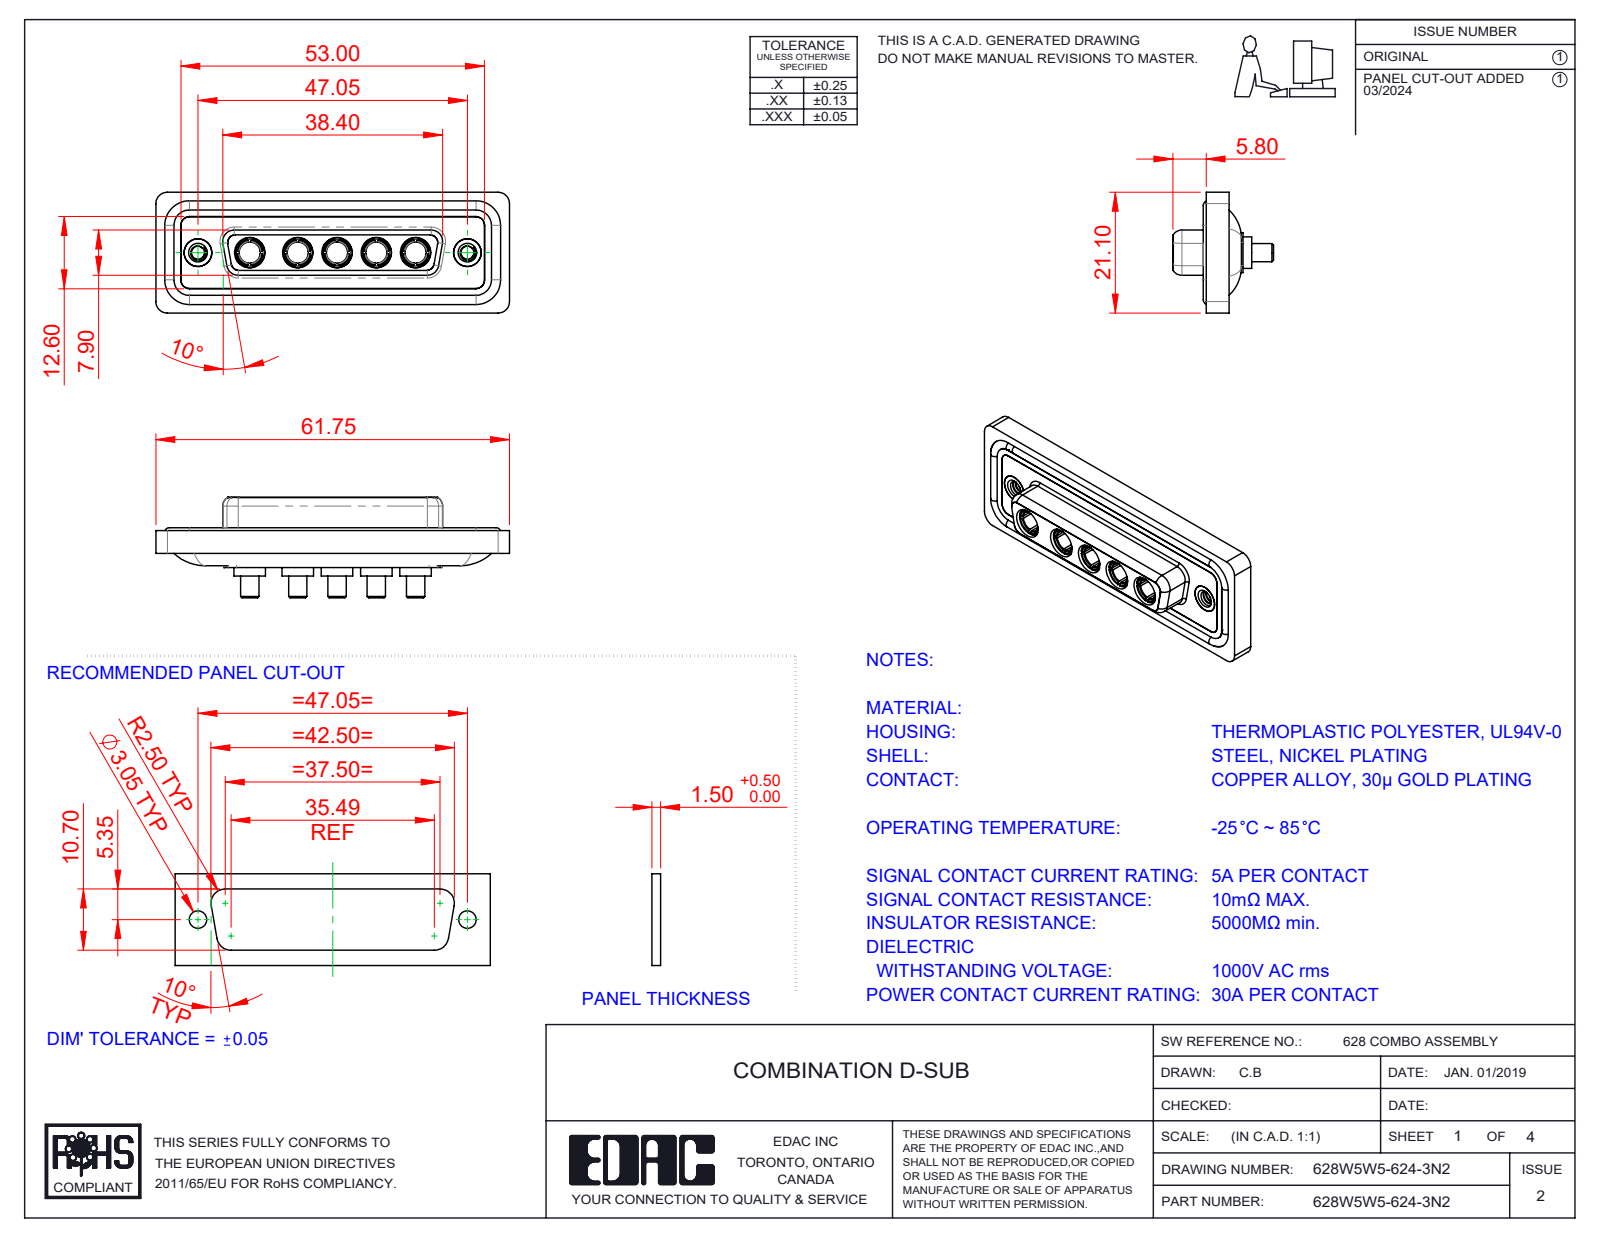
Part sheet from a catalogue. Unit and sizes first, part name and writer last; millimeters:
Units: millimetres
Overall size (bounding box): 61.75 × 21.1 × 17.55
Round holes (diameter × count): ⌀4.85 ×7, ⌀3.7 ×5, ⌀5.3 ×5, ⌀2.26 ×2, ⌀4 ×2, ⌀4.05 ×2, ⌀5 ×2
Round bosses / shafts (diameter × count): ⌀5.5 ×5, ⌀5.2 ×5, ⌀4.96 ×5, ⌀4.75 ×5, ⌀3.75 ×5, ⌀3.2 ×5, ⌀1.6 ×4, ⌀4.95 ×2
Partial cylindrical surfaces — rounded edges, fillets, slot ends (radius × count): R1.5 ×22, R2 ×18, R1.35 ×8, R1.6 ×8, R2.1 ×5, R0.25 ×4, R0.5 ×4, R0.6 ×4
Main face-to-face distances: 0.4, 1.8, 7.45, 5.65, 0.5, 7.05, 6.6, 1.6, 1.1, 2.9
Hole centre spacings: 6.86, 9.04, 13.72, 38.01, 8.39, 15.25, 15.9, 17.43
Volume: 8 208 mm³ · Surface area: 13 438 mm²
Bodies: 17 solids, 756 faces (250 planar, 303 cylindrical, 203 other)
Part name (STEP PRODUCT): 628W5W5-624-3N2; 628Combo Shell Rear_25 Contacts; 628Combo Waterproof Housing_25 Contacts; 628Combo Housing_5W5 (+3 more)
STEP written by: SolidWorks 2023 (CONFIG_CONTROL_DESIGN)
